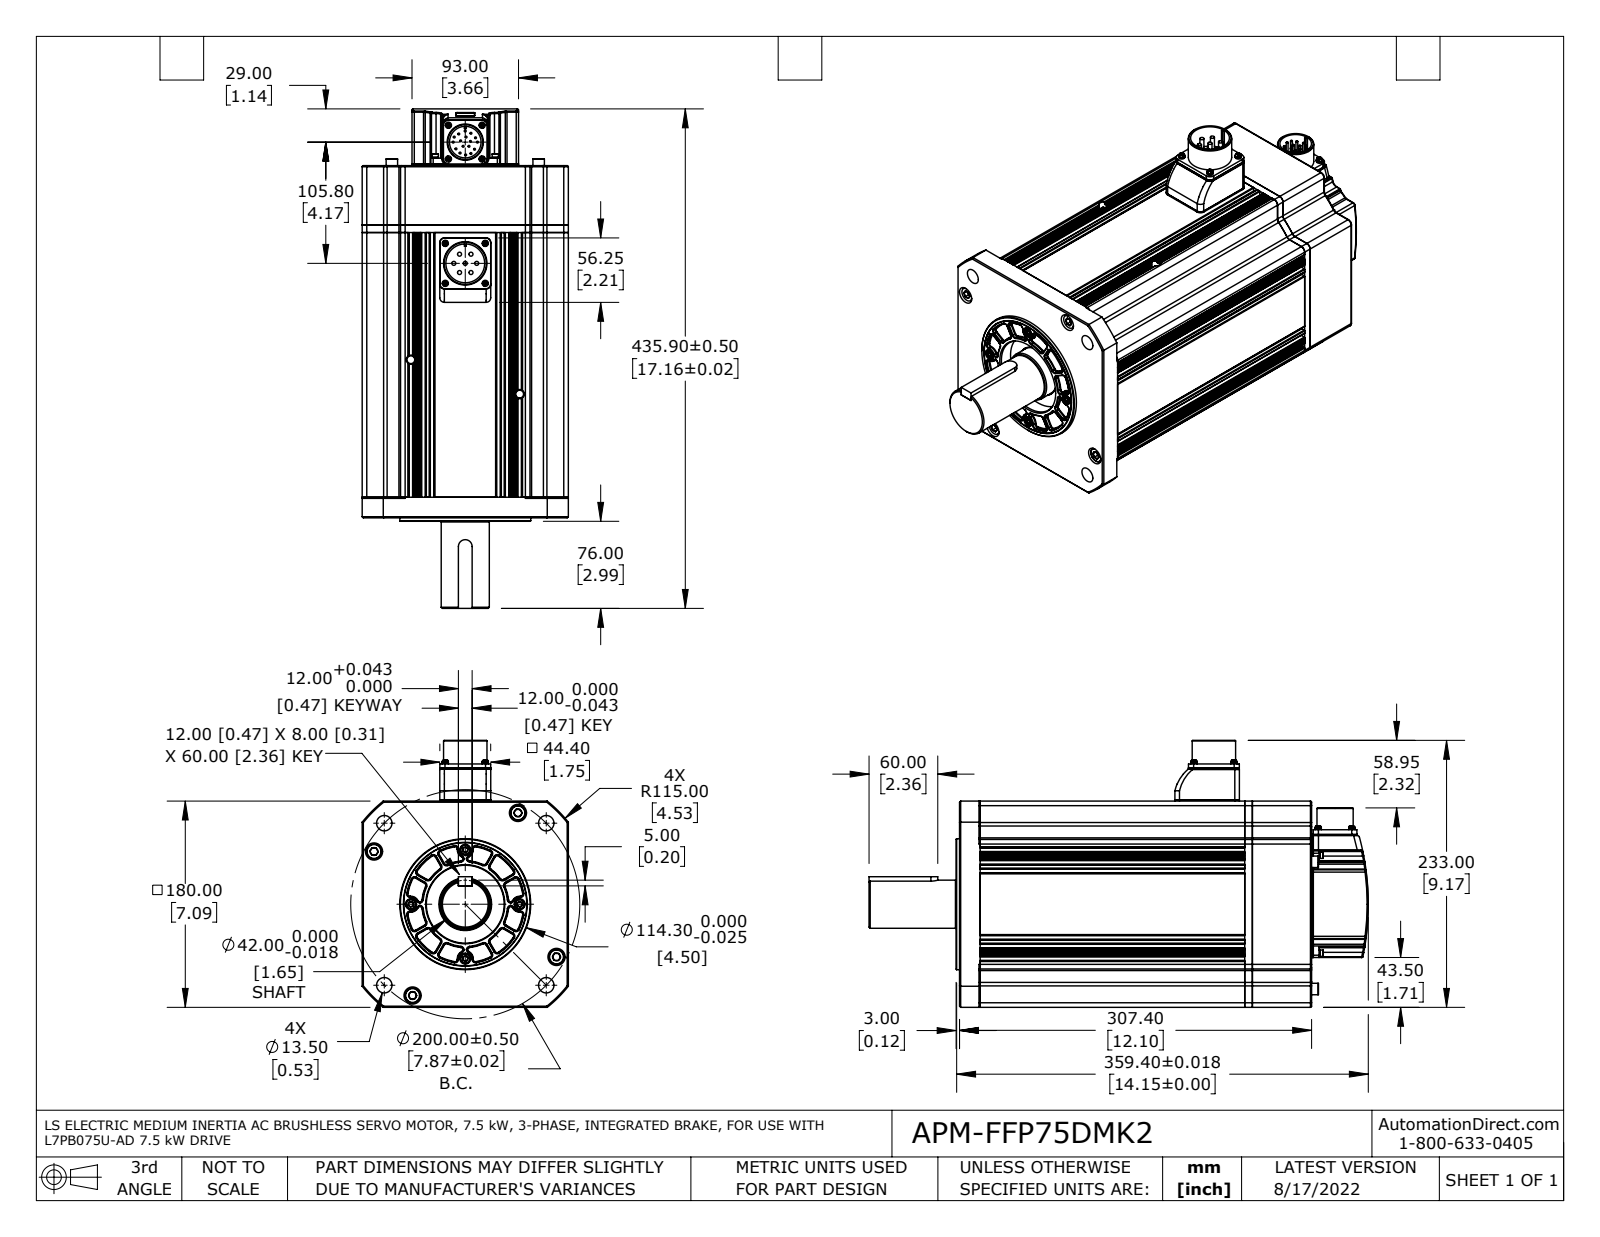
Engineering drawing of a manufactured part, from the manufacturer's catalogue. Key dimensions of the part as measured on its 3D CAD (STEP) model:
Part name (STEP PRODUCT): FMP18GA003G04_Out Line(APM-FFP75D_K2) r1 nc fxt
STEP written by: SolidWorks 2017 (AUTOMOTIVE_DESIGN)
Units: inches
Bodies: 64 solids, 2531 faces (831 planar, 959 cylindrical, 741 other)
Overall size (bounding box): 17.161 × 9.173 × 7.087
Volume: 560.1 in³ · Surface area: 1 045 in²
Round holes (diameter × count): ⌀0.118 ×16, ⌀0.098 ×8, ⌀0.236 ×8, ⌀0.268 ×8, ⌀0.374 ×8, ⌀0.12 ×4, ⌀0.138 ×4, ⌀0.142 ×4, ⌀0.146 ×4, ⌀0.147 ×4, ⌀0.197 ×4, ⌀0.315 ×4
Round bosses / shafts (diameter × count): ⌀0.063 ×17, ⌀0.213 ×8, ⌀0.138 ×7, ⌀0.52 ×4, ⌀0.512 ×4, ⌀0.335 ×4, ⌀0.315 ×4, ⌀0.217 ×4
Partial cylindrical surfaces — rounded edges, fillets, slot ends (radius × count): R0.02 ×124, R0.098 ×56, R0.157 ×24, R0.039 ×22, R0.079 ×17, R0.177 ×12, R0.256 ×4, R0.012 ×2
Main face-to-face distances: 0.264, 9.358, 9.094, 7.087, 5.768, 1.319, 0.039, 0.709, 0.394, 0.315
Hole centre spacings: 1.282, 1.315, 1.343, 2.93, 3.622, 5.423, 1.035, 2.21
